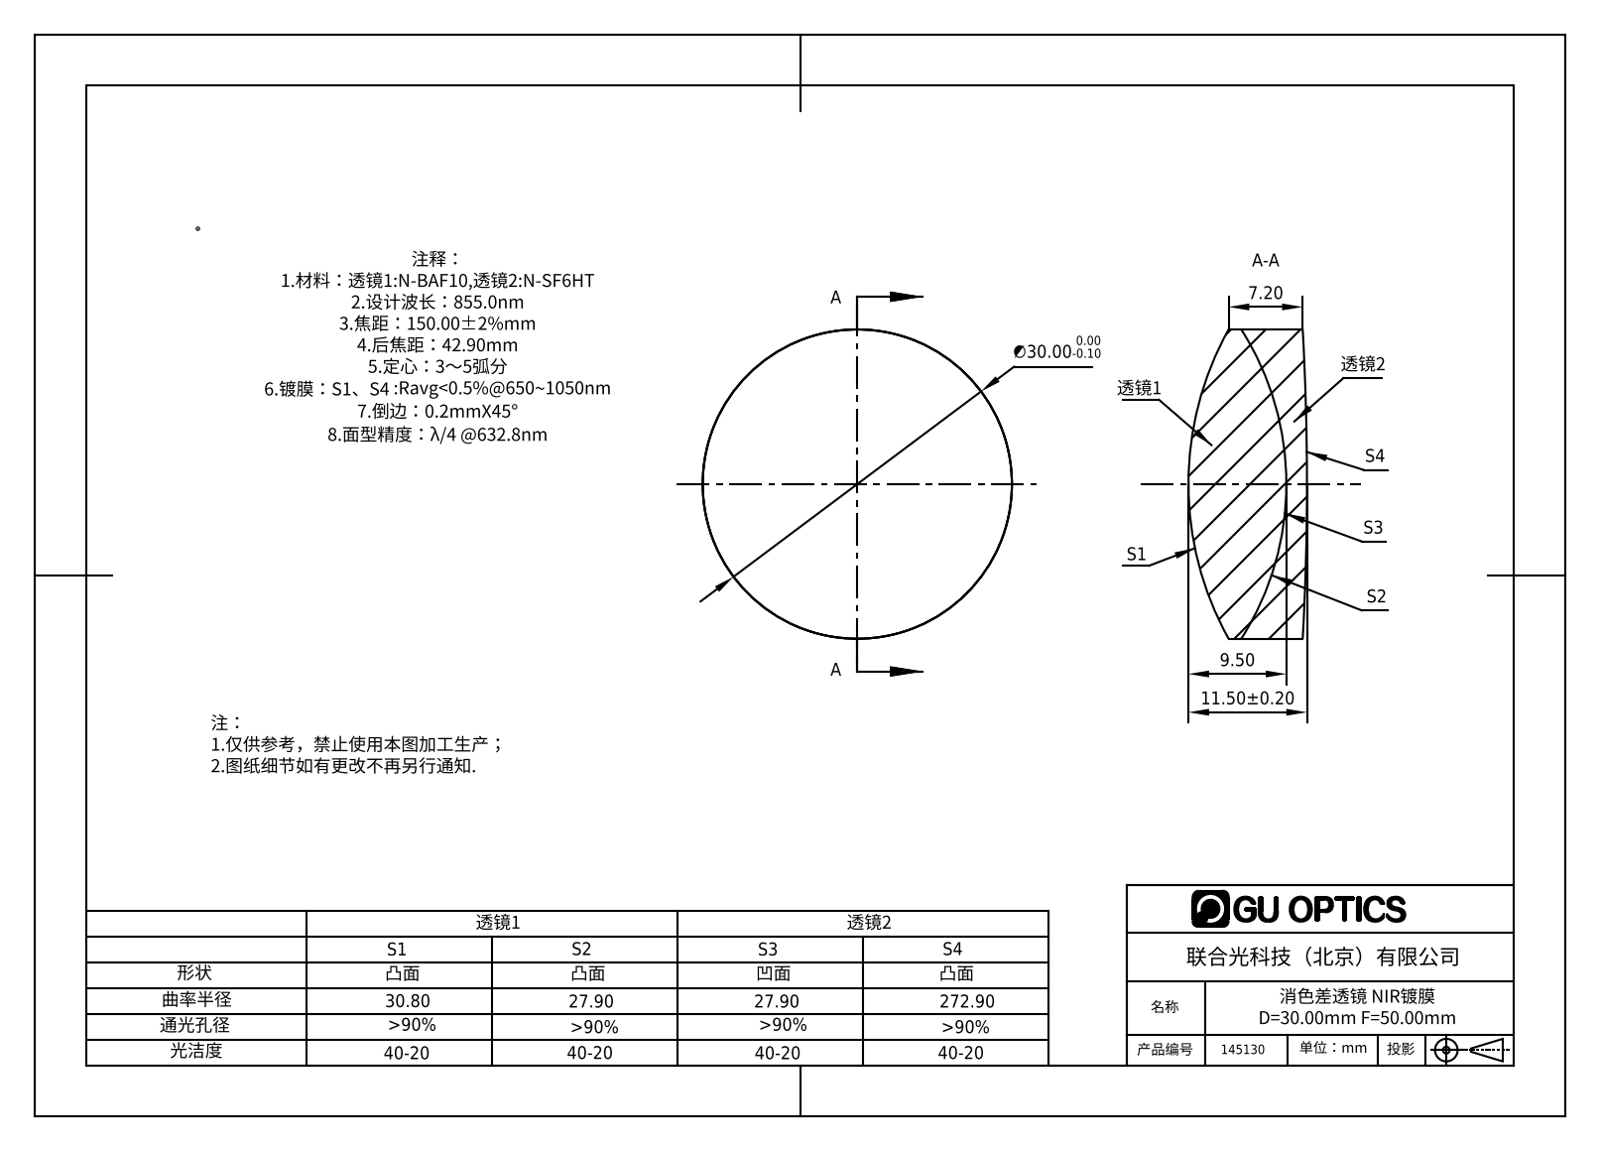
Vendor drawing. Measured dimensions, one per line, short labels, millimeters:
name: 145130
written by: SolidWorks 2016 (AUTOMOTIVE_DESIGN)
unit: mm
bodies: 2 solids, 12 faces (0 planar, 4 cylindrical, 8 other)
size: 30 × 30 × 11.5
volume: 6 636 mm³; area: 3 673 mm²
bosses: 1× ⌀30
